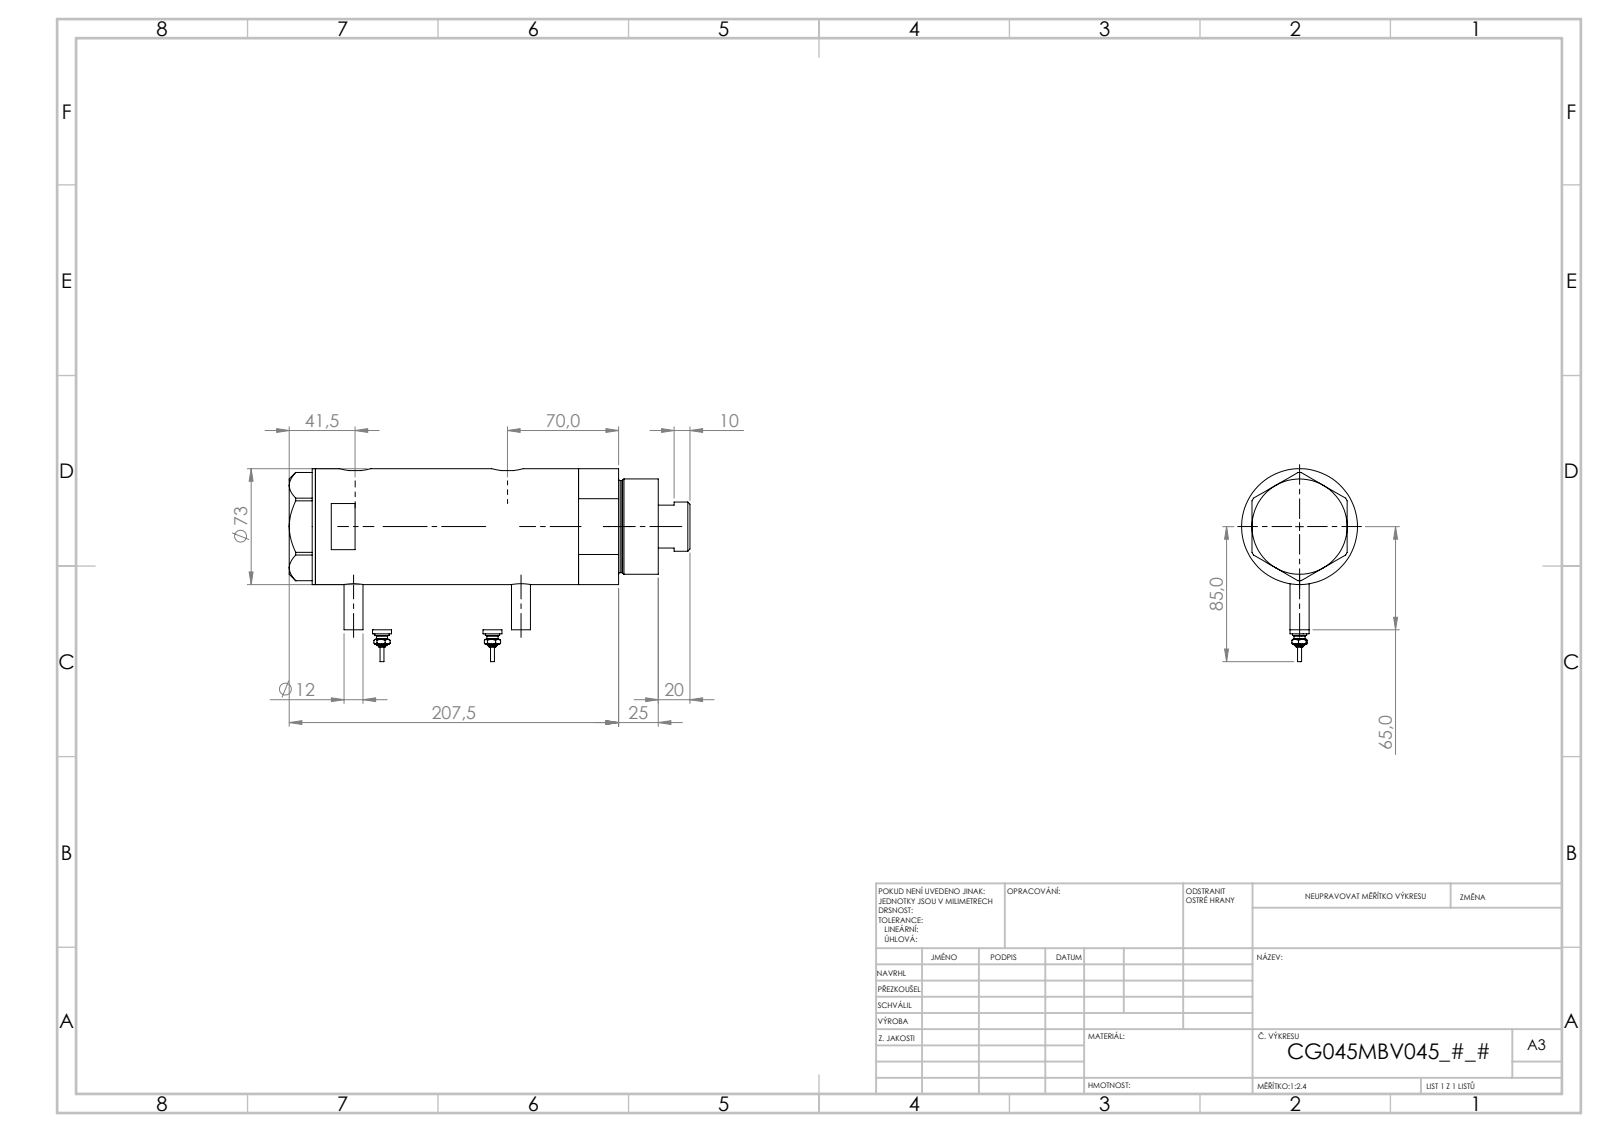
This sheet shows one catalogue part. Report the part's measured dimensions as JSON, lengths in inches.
{"part_name": "V270CG_BACK; V270CG_VC; V270CG_MIDDLE; V270CG_FRONT (+1 more)", "step_written_by": "SolidWorks 2019 (CONFIG_CONTROL_DESIGN)", "units": "inches", "bodies": {"solids": 6, "faces": 231, "planar": 78, "cylindrical": 79, "other": 74}, "overall_size": [9.312, 4.146, 2.874], "volume_in3": 50.2, "surface_area_in2": 221.8, "round_holes": [[0.197, 2], [0.492, 2], [0.518, 2], [0.413, 1], [1.26, 1], [1.319, 1], [1.772, 1], [1.89, 1], [2.52, 1]], "round_bosses_or_shafts": [[0.472, 3], [0.354, 2], [0.276, 2], [0.171, 2], [0.094, 2], [2.874, 1], [2.362, 1], [2.283, 1]], "partial_cylinders_radius": [[0.394, 2]], "face_to_face_distances": [4.415, 1.024, 3.391, 0.65, 1.673, 5.065, 7.874, 8.524, 6.851, 3.459], "hole_center_spacings": [3.805, 0.039, 0.039, 0.335, 0.335, 3.431, 3.47, 3.47]}
